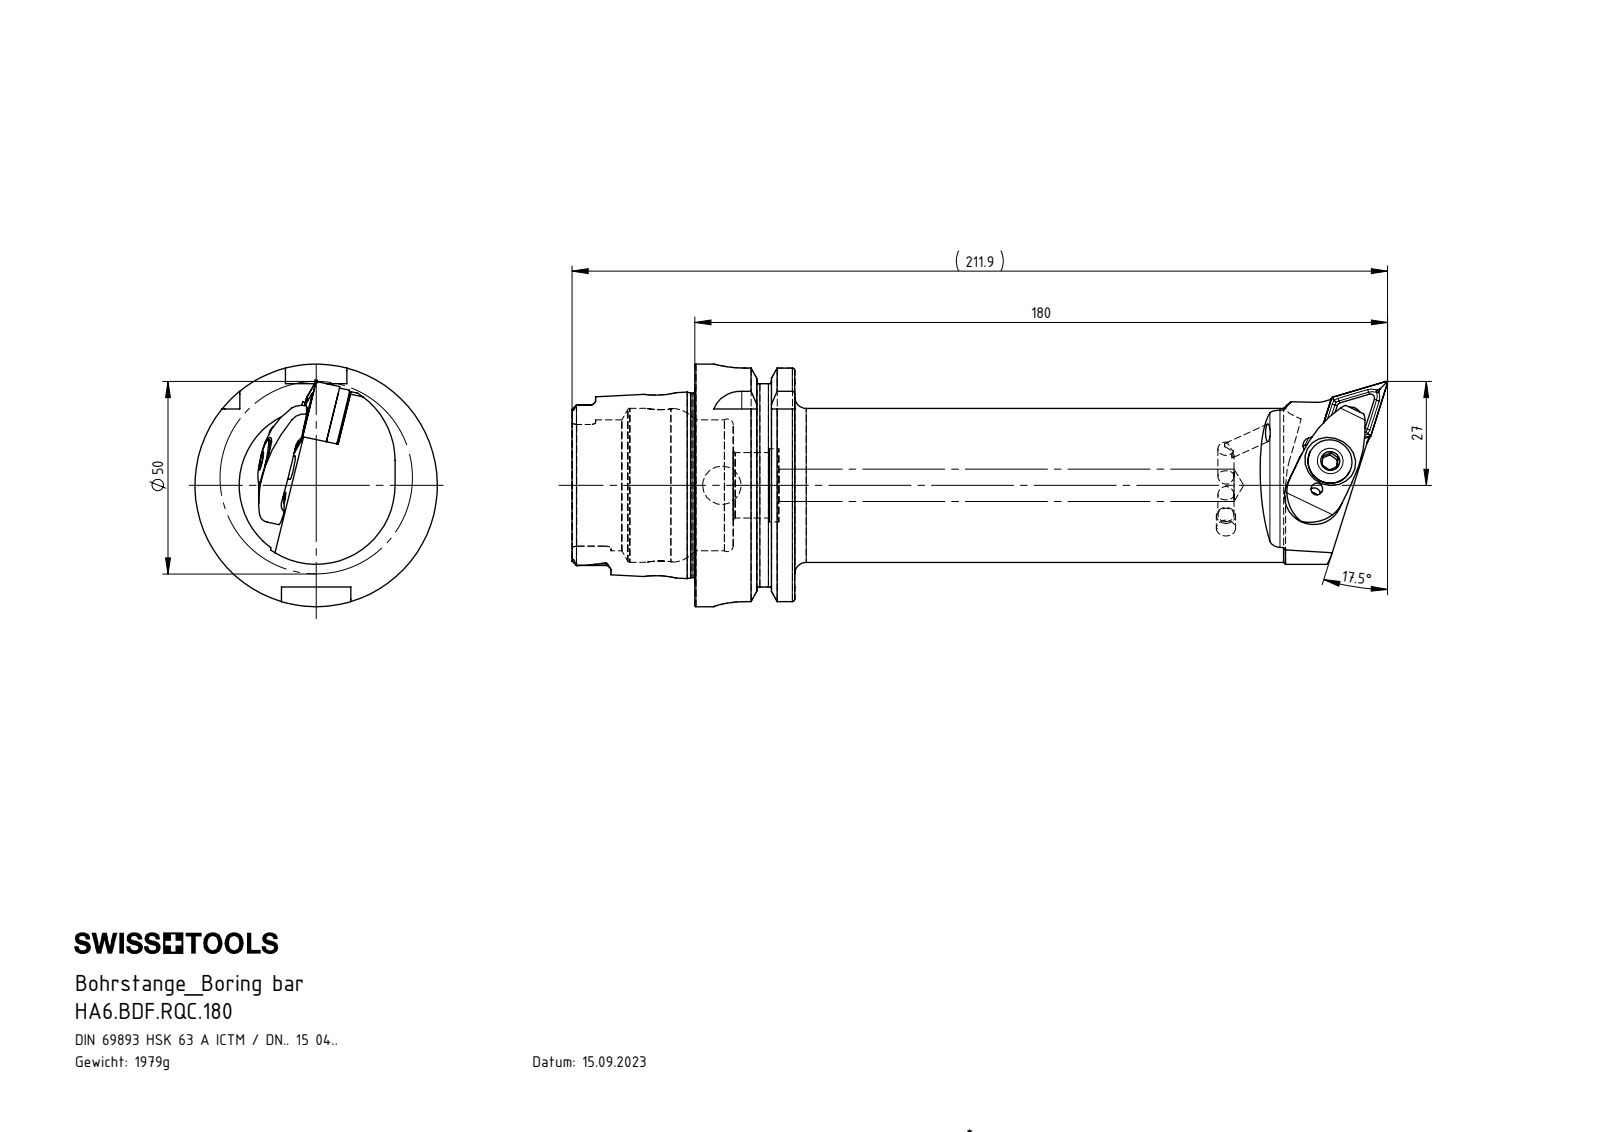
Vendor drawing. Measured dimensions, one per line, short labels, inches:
name: WCC-ER2.001.010_A; WCC-ER4.102.020_A; DNMG150604; HA6-BDF.RQC.180_E (+5 more)
written by: SolidWorks 2017 (AUTOMOTIVE_DESIGN)
unit: in
bodies: 9 solids, 412 faces (111 planar, 133 cylindrical, 168 other)
size: 8.343 × 2.48 × 2.48
volume: 15.44 in³; area: 75.15 in²
holes: 3× ⌀0.165, 2× ⌀0.197, 1× ⌀0.118, 1× ⌀0.157, 1× ⌀0.203, 1× ⌀0.256, 1× ⌀0.276, 1× ⌀0.295, 1× ⌀0.331, 1× ⌀0.394, 1× ⌀0.669, 1× ⌀0.748
bosses: 2× ⌀0.197, 1× ⌀2.48, 1× ⌀2.163, 1× ⌀1.887, 1× ⌀0.453, 1× ⌀0.276, 1× ⌀0.244, 1× ⌀0.236
rounds: 6× R0.015, 6× R0.027, 6× R0.055, 5× R0.016, 4× R0.315, 3× R0.118, 2× R0.079, 2× R0.111
face distances: 1.022, 0.63, 0.392, 1.256, 1.648, 2.278, 0.238, 2.079, 0.858, 0.125
hole spacings: 0.591, 0.906, 0.315, 0.323, 0.583, 0.583
